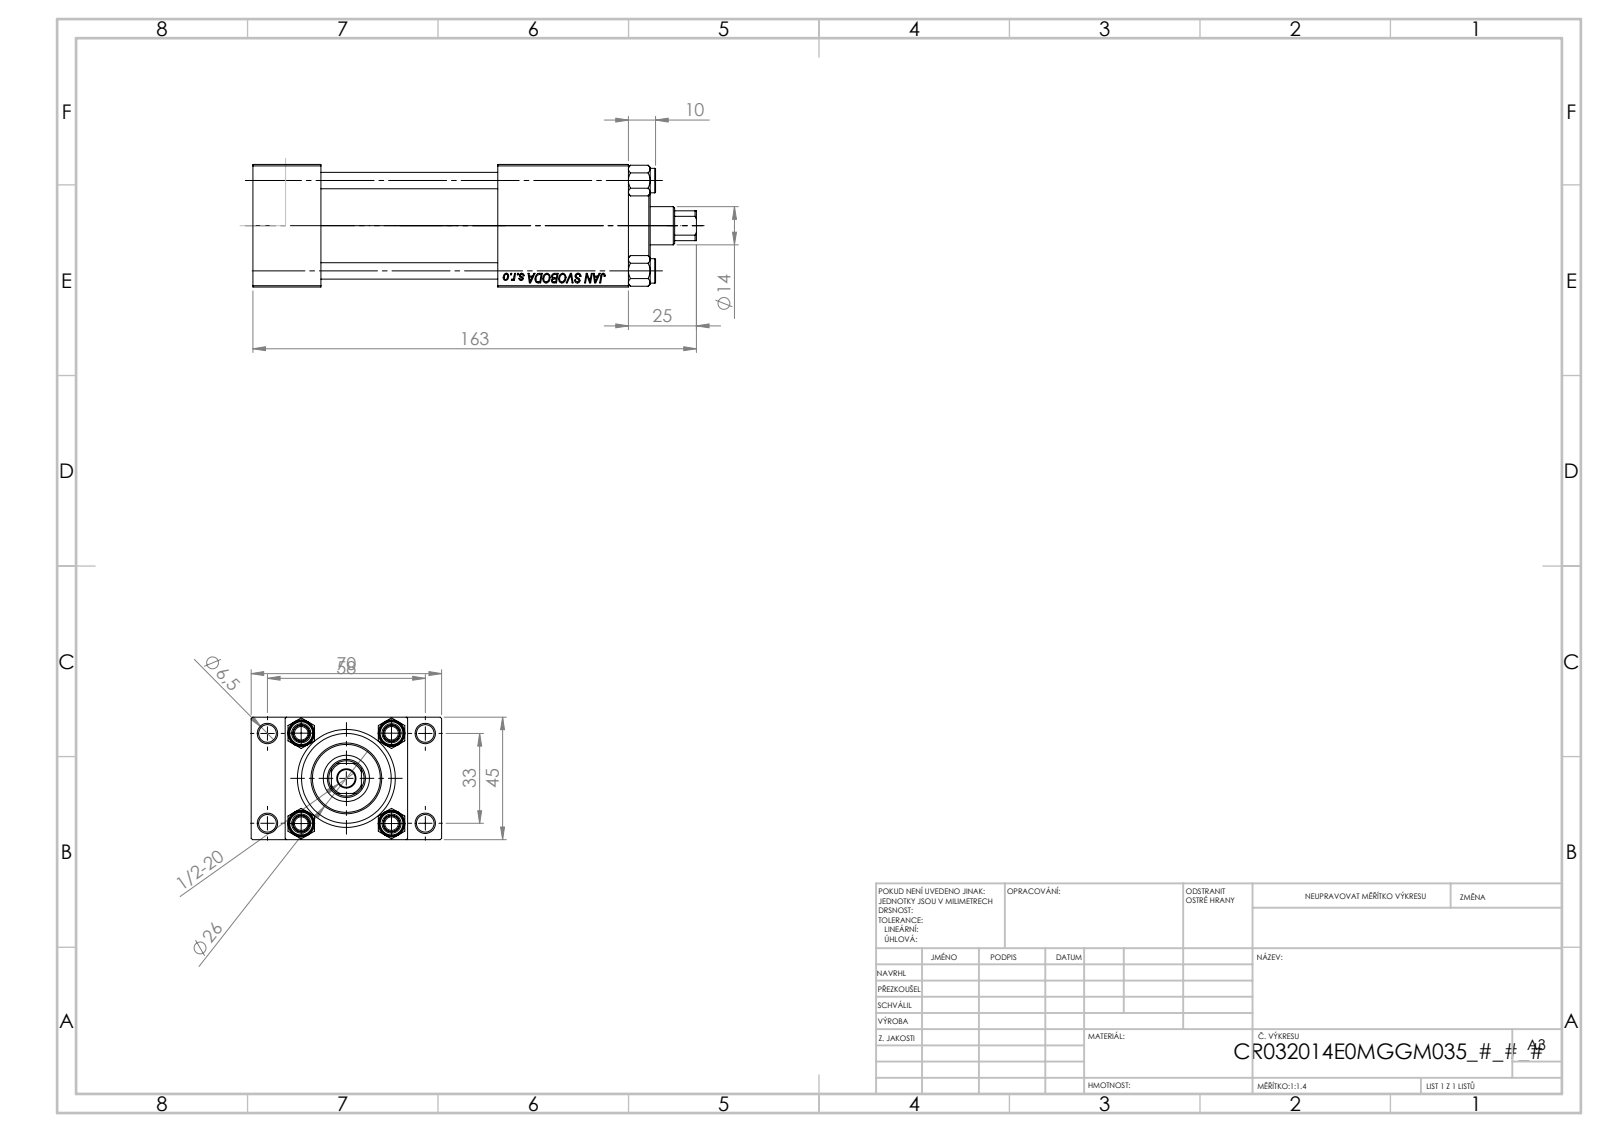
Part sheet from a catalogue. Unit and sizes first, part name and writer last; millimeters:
Units: millimetres
Overall size (bounding box): 163 × 70 × 45
Round holes (diameter × count): ⌀6.5 ×5, ⌀6 ×4, ⌀7 ×2, ⌀13.16 ×2, ⌀20 ×2, ⌀14 ×1, ⌀17 ×1, ⌀24 ×1, ⌀32 ×1, ⌀33 ×1
Round bosses / shafts (diameter × count): ⌀9 ×4, ⌀38 ×1, ⌀26 ×1
Partial cylindrical surfaces — rounded edges, fillets, slot ends (radius × count): R6.5 ×1
Main face-to-face distances: 45, 25, 12.5, 57.5, 138, 113, 65, 70, 90, 48
Hole centre spacings: 12.4, 23.48, 33.2, 33.37, 35.35, 45.6, 56.35, 33
Volume: 229 027 mm³ · Surface area: 81 162 mm²
Bodies: 11 solids, 1136 faces (497 planar, 87 cylindrical, 552 other)
Part name (STEP PRODUCT): V215CR_E_Body; V215CR_TYCINKA_E; V215_VC_A; NUT_M5_E (+1 more)
STEP written by: SolidWorks 2019 (CONFIG_CONTROL_DESIGN)
